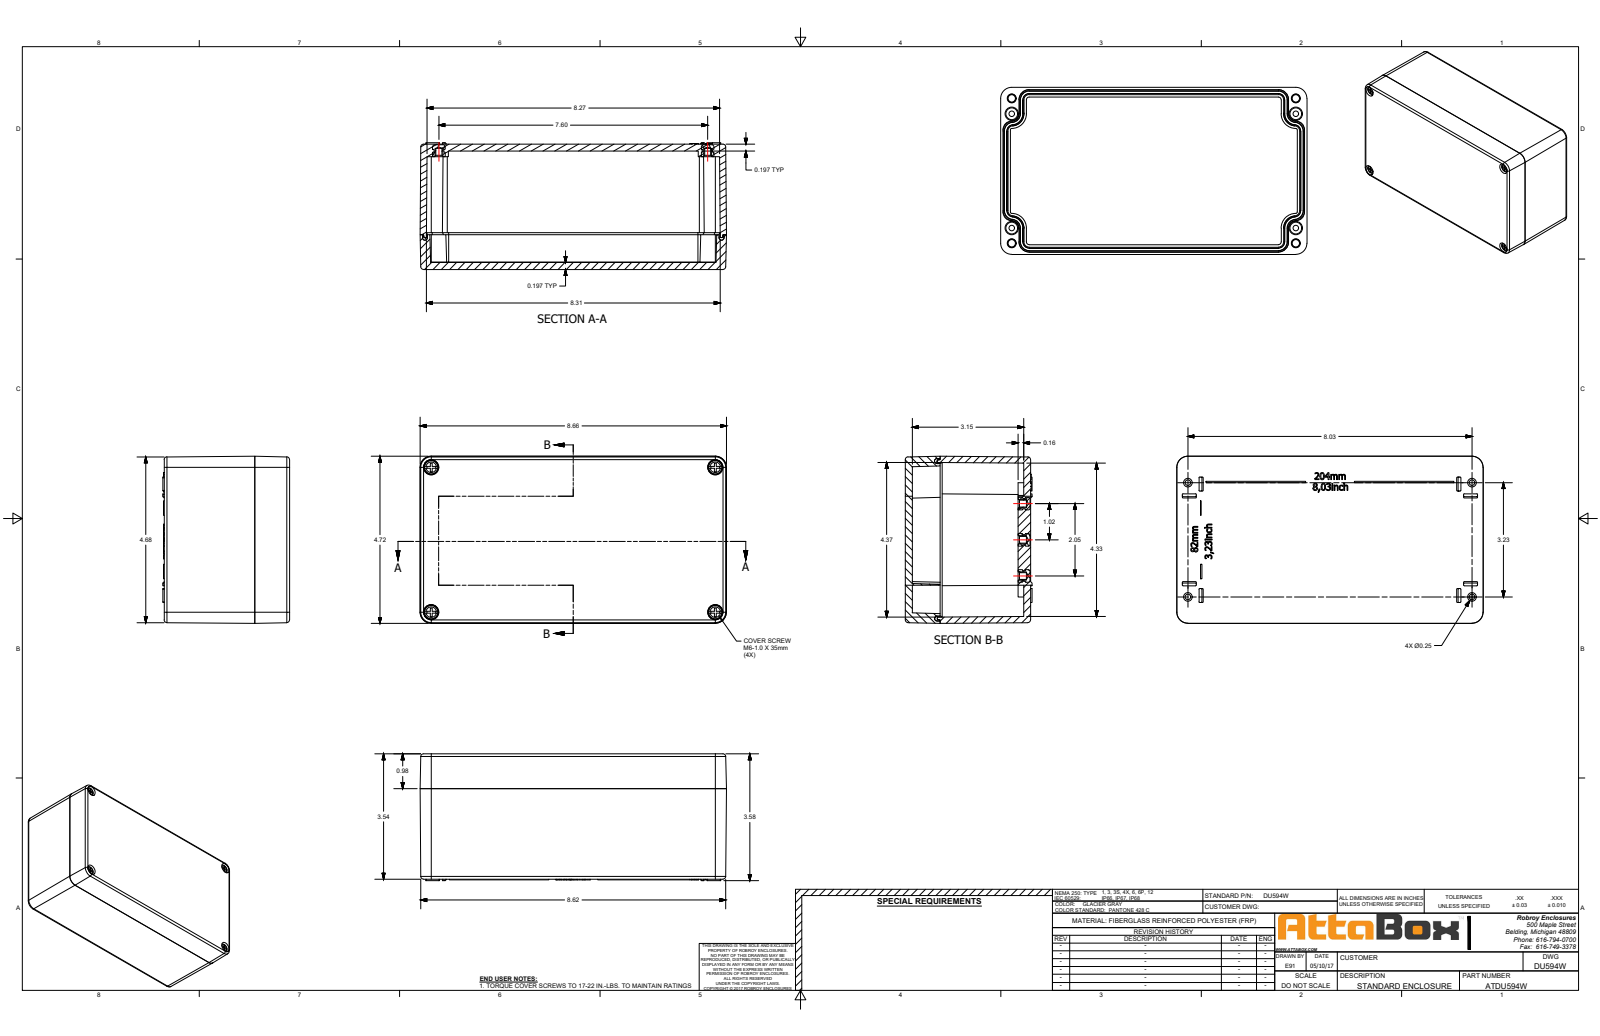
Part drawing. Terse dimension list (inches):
name: DU594W
written by: SolidWorks 2018 (AUTOMOTIVE_DESIGN)
unit: in
bodies: 17 solids, 1290 faces (626 planar, 174 cylindrical, 490 other)
size: 8.661 × 4.724 × 3.583
volume: 36 in³; area: 397 in²
holes: 10× ⌀0.194, 6× ⌀0.236, 4× ⌀0.213, 4× ⌀0.276
bosses: 10× ⌀0.291, 4× ⌀0.374, 4× ⌀0.315, 4× ⌀0.236, 4× ⌀0.205
rounds: 32× R0.02, 12× R0.069, 8× R0.148, 8× R0.285, 6× R0.016, 4× R0.078, 4× R0.079, 4× R0.108
face distances: 3.346, 0.197, 0.177, 3.543, 3.15, 0.984, 2.362, 0.787, 2.559, 0.453
hole spacings: 1.024, 1.046, 2.059, 3.078, 7.667, 7.882, 8.079, 8.397
